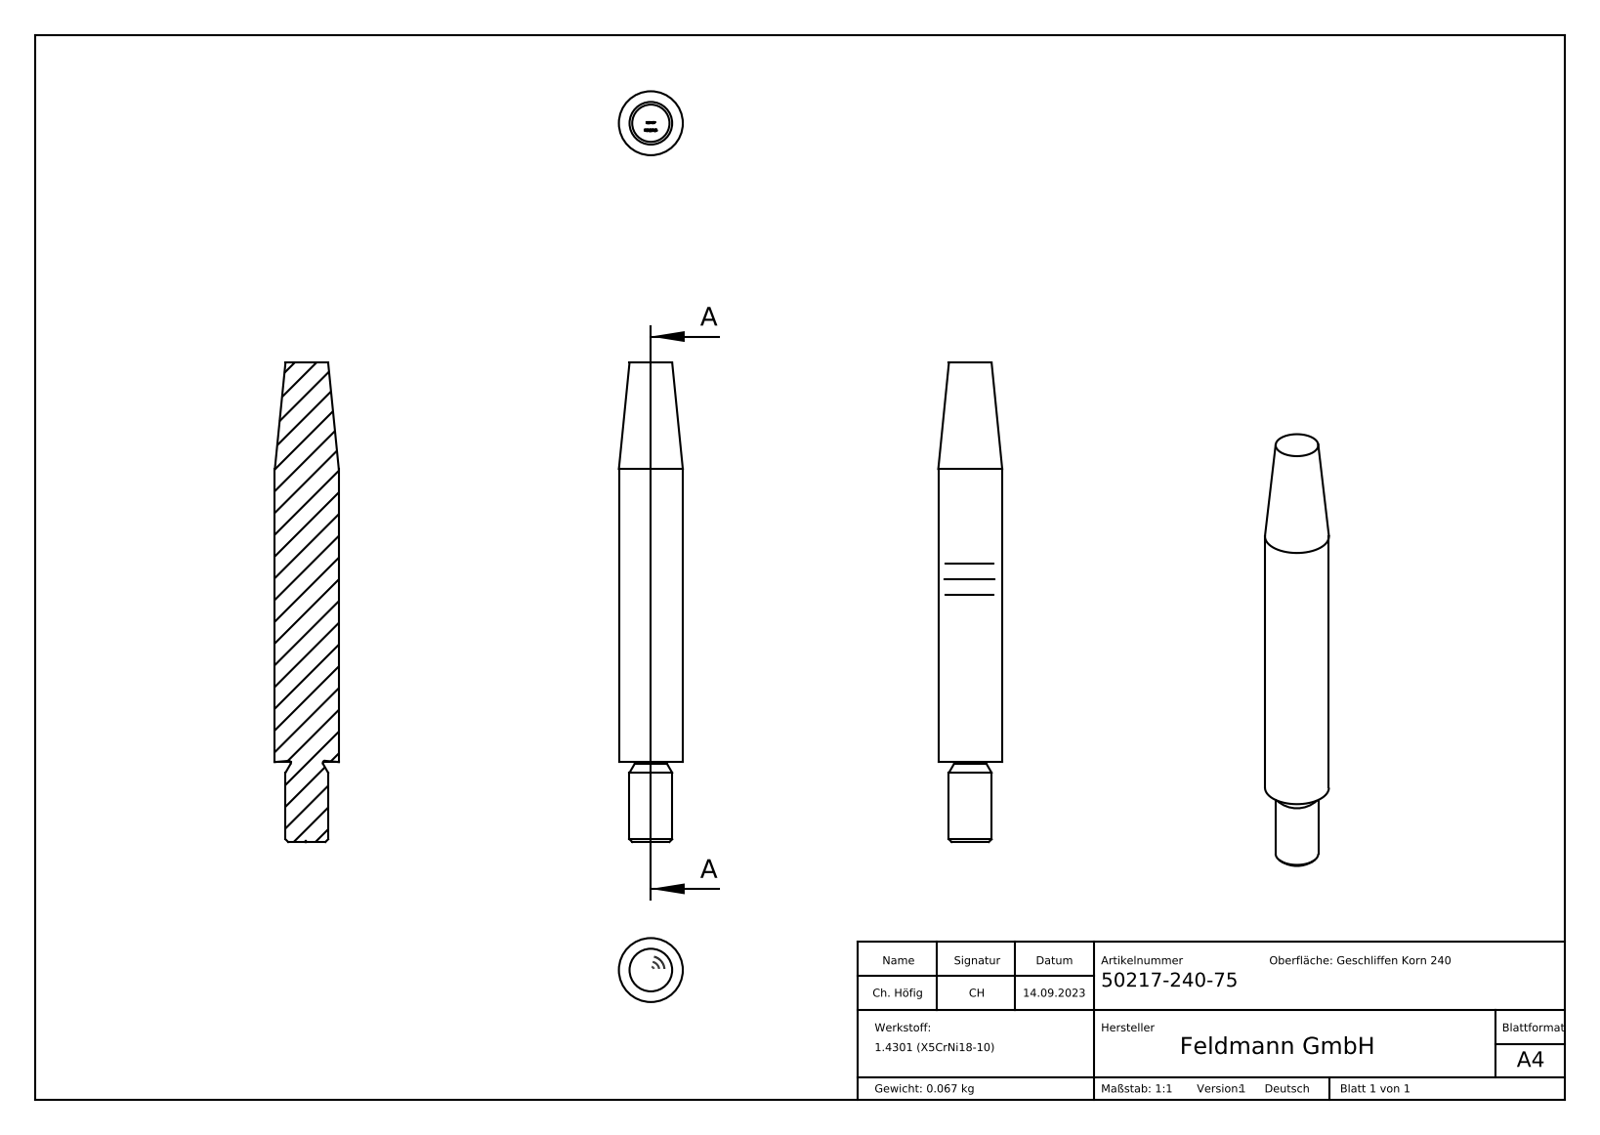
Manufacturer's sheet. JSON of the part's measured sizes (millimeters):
{"part_name": "50217-240-75", "step_written_by": "SolidWorks 2018 (CONFIG_CONTROL_DESIGN)", "units": "millimeters", "bodies": {"solids": 1, "faces": 246, "planar": 145, "cylindrical": 2, "other": 99}, "overall_size": [90, 12, 12], "volume_mm3": 8528, "surface_area_mm2": 3262, "round_bosses_or_shafts": [[12, 1], [8, 1]], "face_to_face_distances": [90, 89.9, 0.33, 0.54, 1.44, 0.94, 0.79, 0.59, 1.33, 0.91]}
